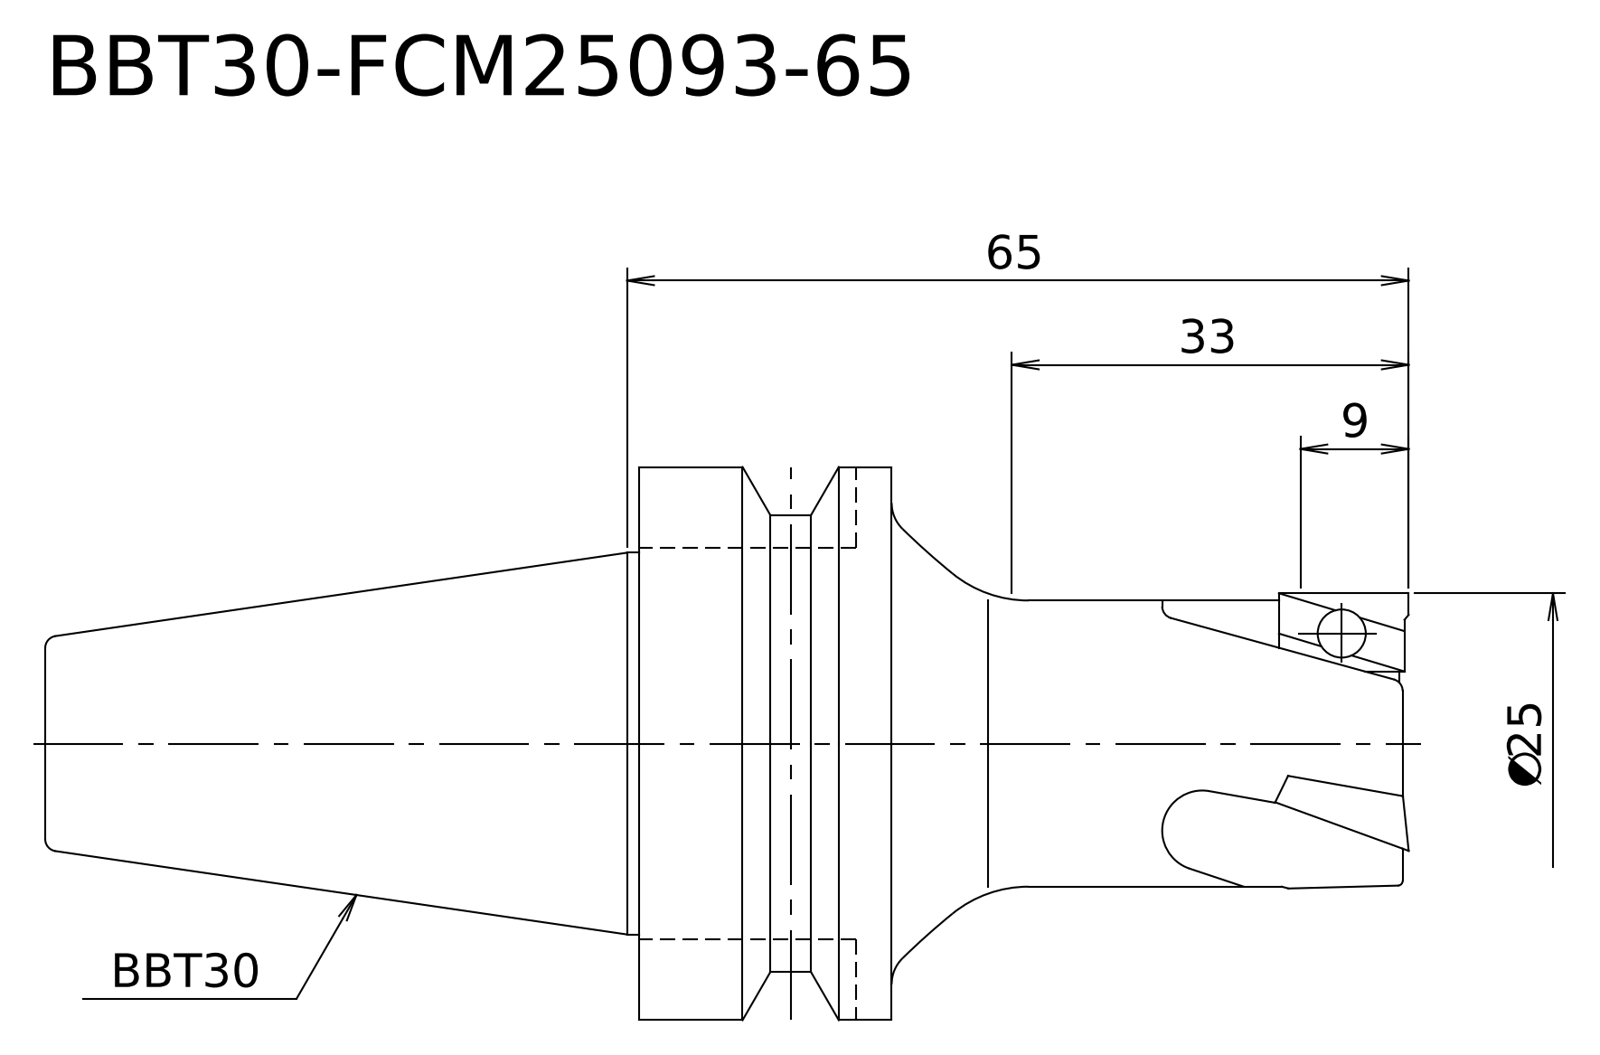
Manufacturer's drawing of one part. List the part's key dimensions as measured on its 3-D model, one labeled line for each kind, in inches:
STEP written by: Kubotek KeyCreator V8.5.1 (14335) (CONFIG_CONTROL_DESIGN)
Units: inches
Bodies: 1 solid, 17 faces (4 planar, 6 cylindrical, 7 other)
Overall size (bounding box): 4.465 × 1.811 × 1.811
Volume: 4.804 in³ · Surface area: 20.46 in²
Round bosses / shafts (diameter × count): ⌀1.811 ×1, ⌀1.496 ×1, ⌀1.25 ×1, ⌀0.984 ×1, ⌀0.937 ×1
Main face-to-face distances: 2.52, 1.693, 0.827, 4.465, 2.772, 1.945
